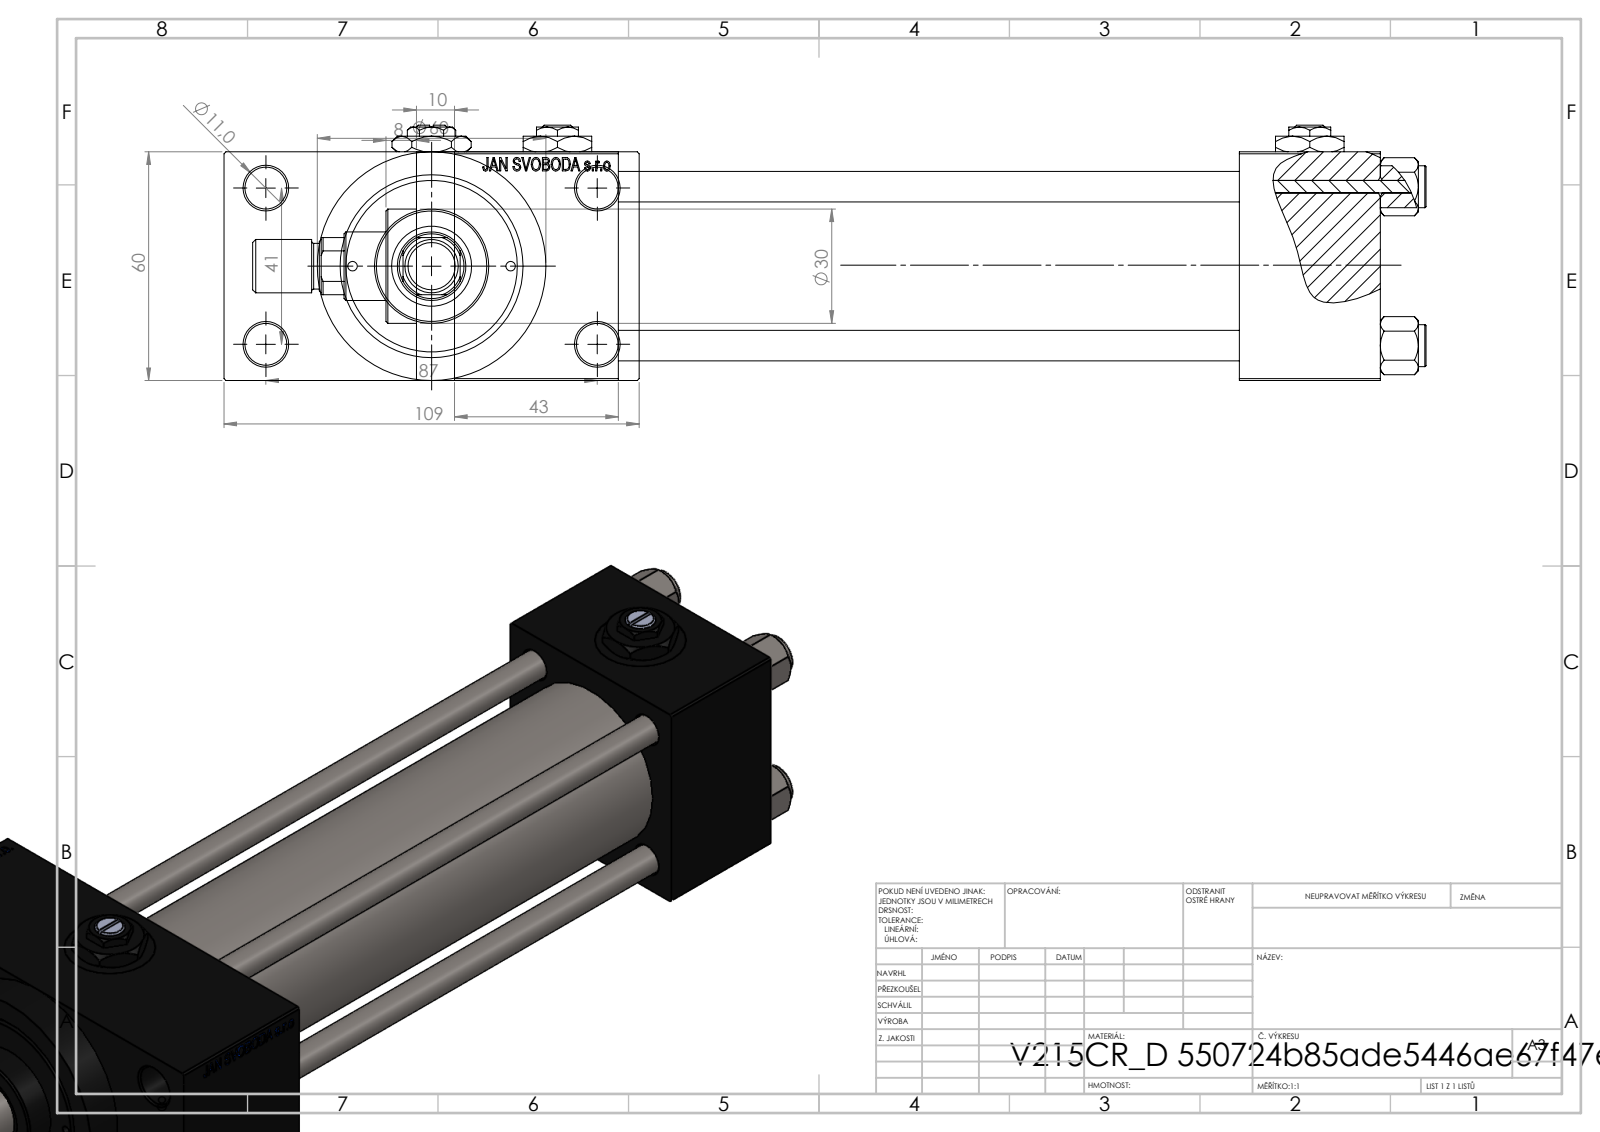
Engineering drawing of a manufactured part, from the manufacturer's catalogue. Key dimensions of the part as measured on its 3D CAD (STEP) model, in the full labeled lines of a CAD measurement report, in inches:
Part name (STEP PRODUCT): Zatka_pro_OIL_PORT; V215CR_D_Body; V215CR_D_TYCINKA; ROD_END_AH (+3 more)
STEP written by: SolidWorks 2019 (CONFIG_CONTROL_DESIGN)
Units: inches
Bodies: 14 solids, 1227 faces (552 planar, 107 cylindrical, 568 other)
Overall size (bounding box): 12.126 × 4.291 × 2.638
Volume: 36.81 in³ · Surface area: 265.3 in²
Round holes (diameter × count): ⌀0.315 ×4, ⌀0.433 ×4, ⌀0.656 ×4, ⌀0.945 ×4, ⌀0.276 ×3, ⌀0.098 ×2, ⌀0.335 ×1, ⌀0.709 ×1, ⌀0.827 ×1, ⌀1.22 ×1, ⌀1.575 ×1, ⌀1.772 ×1
Round bosses / shafts (diameter × count): ⌀0.433 ×4, ⌀2.362 ×1, ⌀1.811 ×1, ⌀1.181 ×1, ⌀0.551 ×1, ⌀0.472 ×1
Partial cylindrical surfaces — rounded edges, fillets, slot ends (radius × count): R0.335 ×1
Main face-to-face distances: 2.362, 6.417, 0.965, 3.327, 1.457, 7.874, 1.693, 9.567, 8.11, 2.087
Hole centre spacings: 0.821, 0.892, 1.161, 1.206, 1.642, 1.832, 1.856, 1.893
